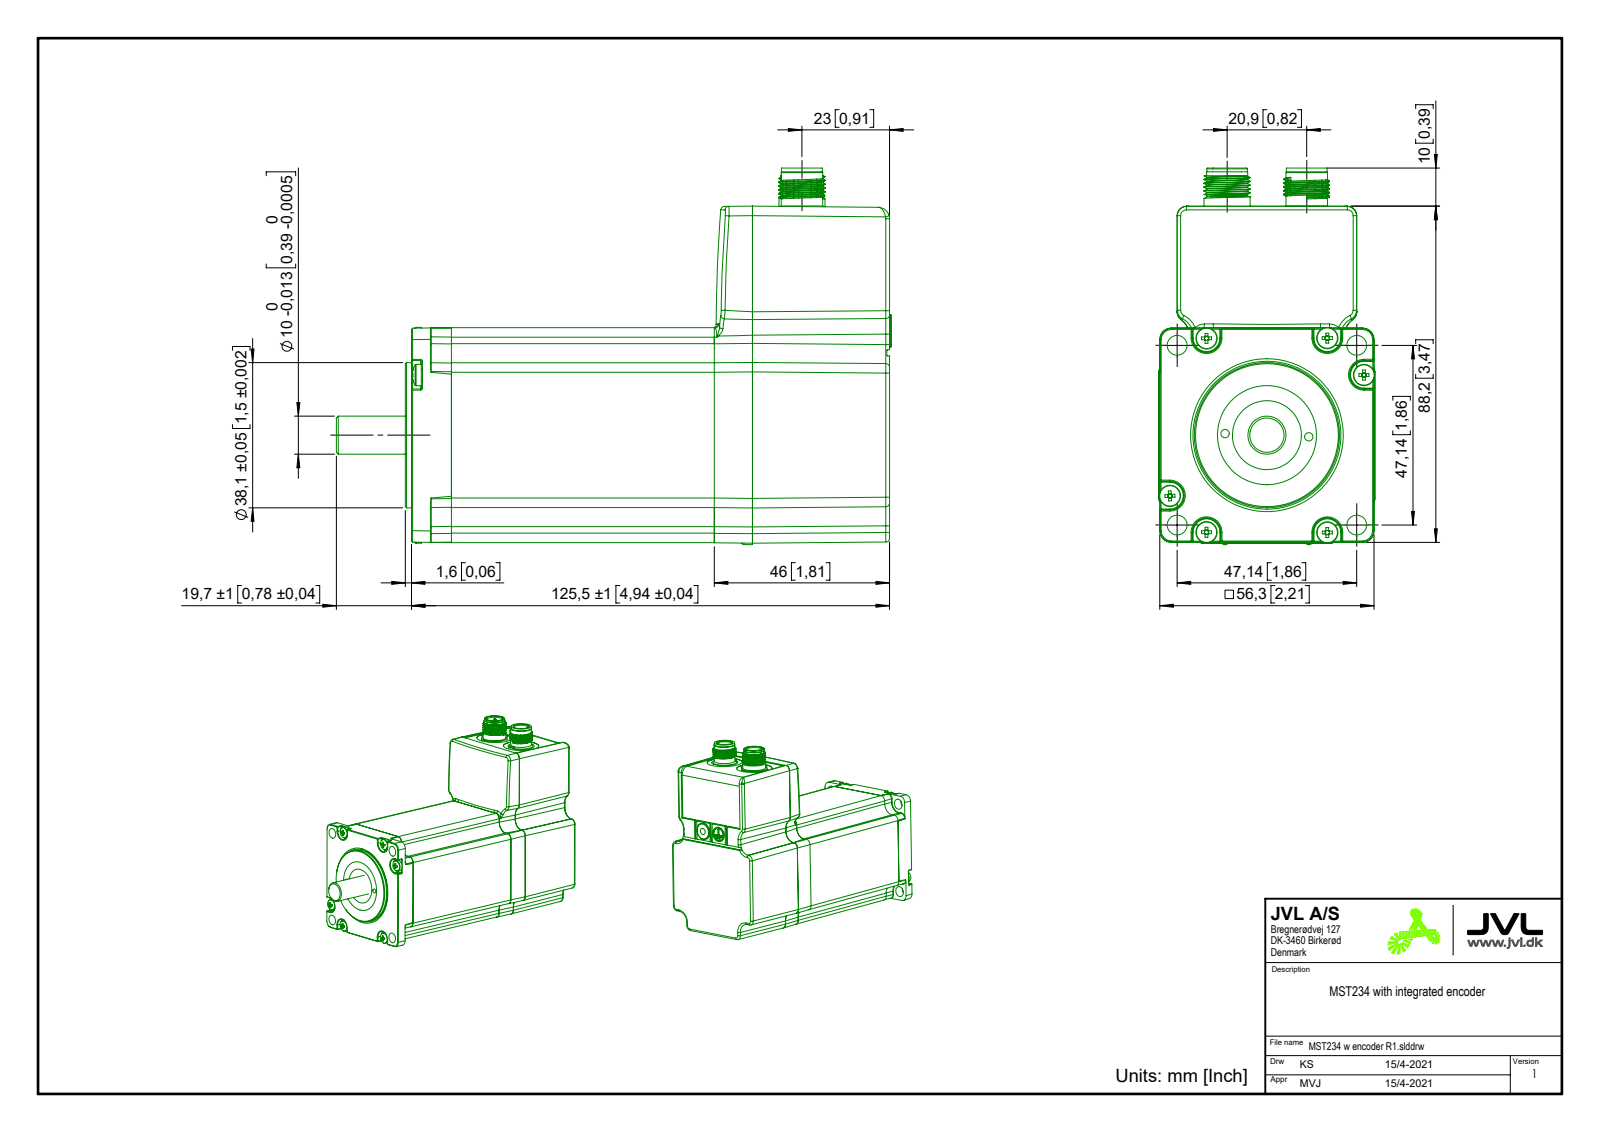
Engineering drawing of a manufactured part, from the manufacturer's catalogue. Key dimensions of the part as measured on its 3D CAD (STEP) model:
Part name (STEP PRODUCT): MST234 w encoder R1
STEP written by: SolidWorks 2020 (AUTOMOTIVE_DESIGN)
Units: millimetres
Bodies: 1 solid, 1216 faces (388 planar, 302 cylindrical, 526 other)
Overall size (bounding box): 145.7 × 98.83 × 56.67
Volume: 426 446 mm³ · Surface area: 44 132 mm²
Round holes (diameter × count): ⌀1.1 ×8, ⌀2.5 ×6, ⌀2.2 ×2, ⌀18.5 ×2, ⌀3.3 ×1, ⌀6.76 ×1, ⌀8.2 ×1, ⌀8.3 ×1, ⌀18.1 ×1, ⌀26 ×1
Round bosses / shafts (diameter × count): ⌀0.8 ×8, ⌀5.6 ×6, ⌀3 ×6, ⌀1 ×5, ⌀38.1 ×1, ⌀12.1 ×1, ⌀12.1 ×1, ⌀10.9 ×1
Partial cylindrical surfaces — rounded edges, fillets, slot ends (radius × count): R0.2 ×34, R2.5 ×29, R5 ×18, R0.3 ×16, R1 ×11, R2.3 ×8, R3 ×5, R0.8 ×4
Main face-to-face distances: 56.4, 4.75, 125.5, 0.7, 124.8, 51.92, 9.2, 47.2, 56.67, 1.6
Hole centre spacings: 2.74, 30, 2.75, 42.43, 2.32, 4.21, 60, 2.33
